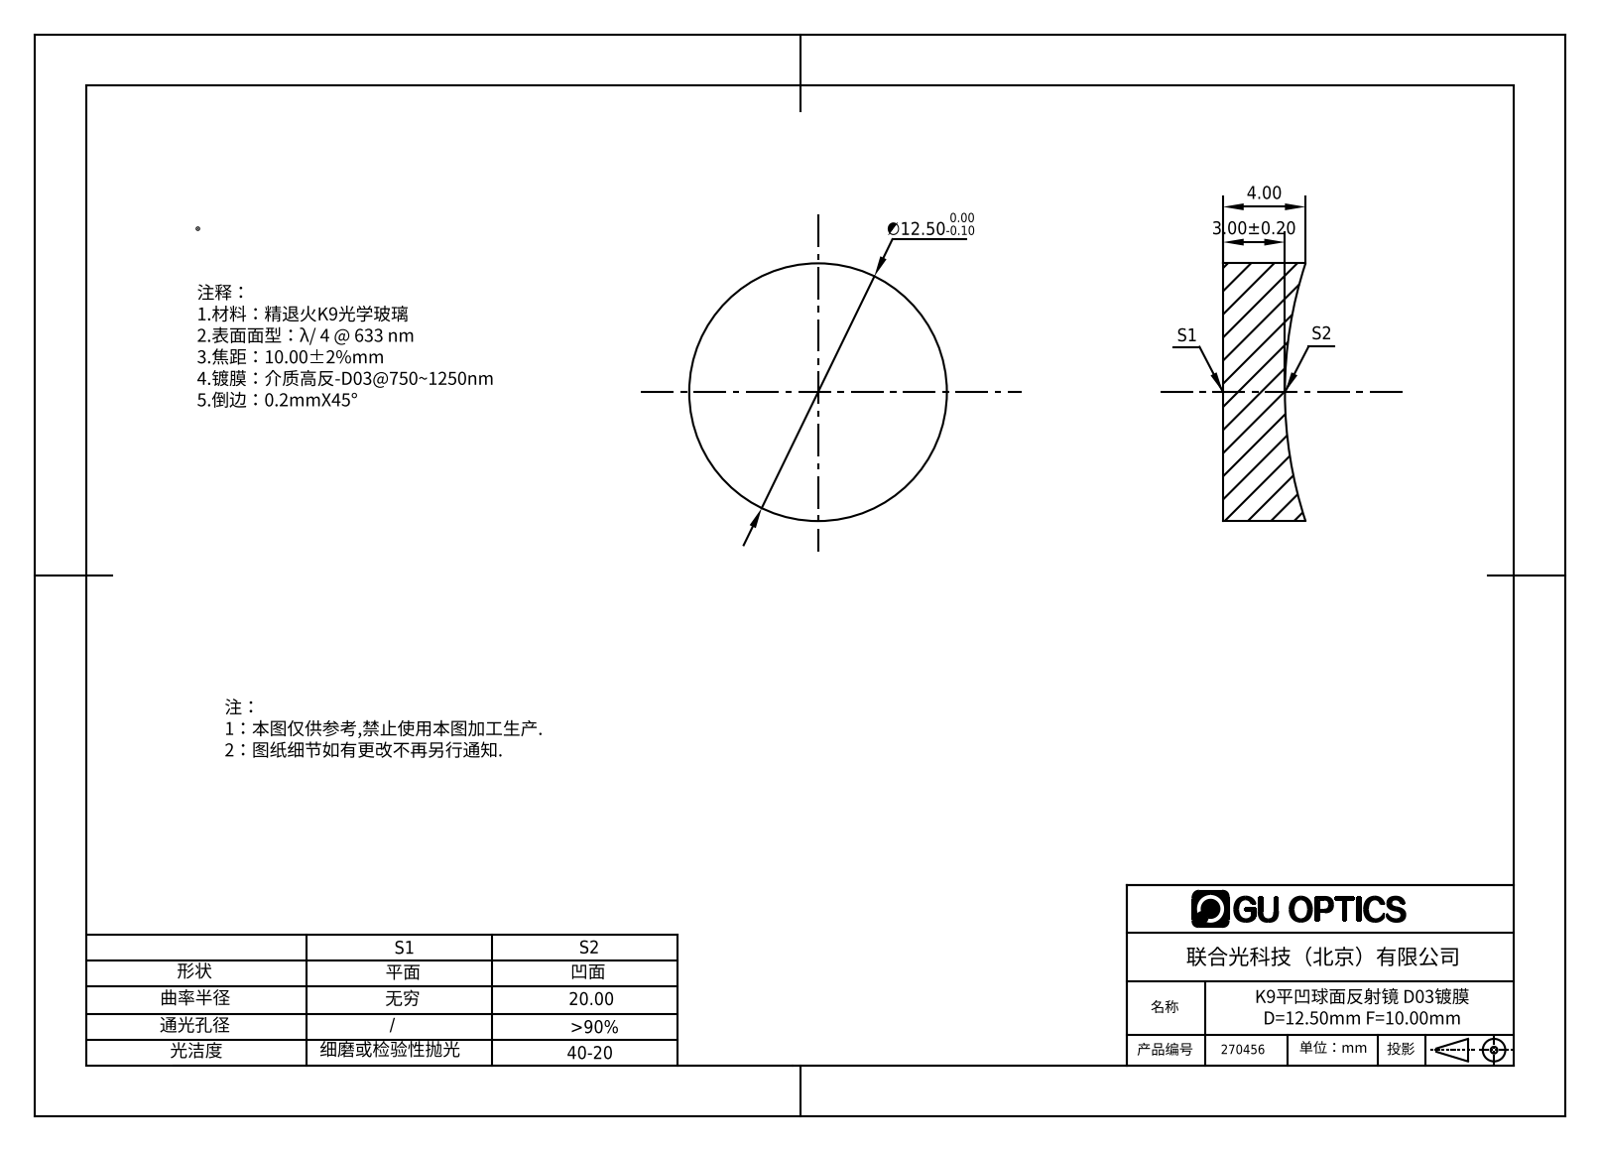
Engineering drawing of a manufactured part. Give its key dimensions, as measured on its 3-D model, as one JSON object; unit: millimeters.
{"part_name": "270001", "step_written_by": "SolidWorks 2016 (AUTOMOTIVE_DESIGN)", "units": "millimeters", "bodies": {"solids": 1, "faces": 5, "planar": 1, "cylindrical": 2, "other": 2}, "overall_size": [12.5, 12.5, 4], "volume_mm3": 429, "surface_area_mm2": 406, "round_bosses_or_shafts": [[12.5, 1]]}
